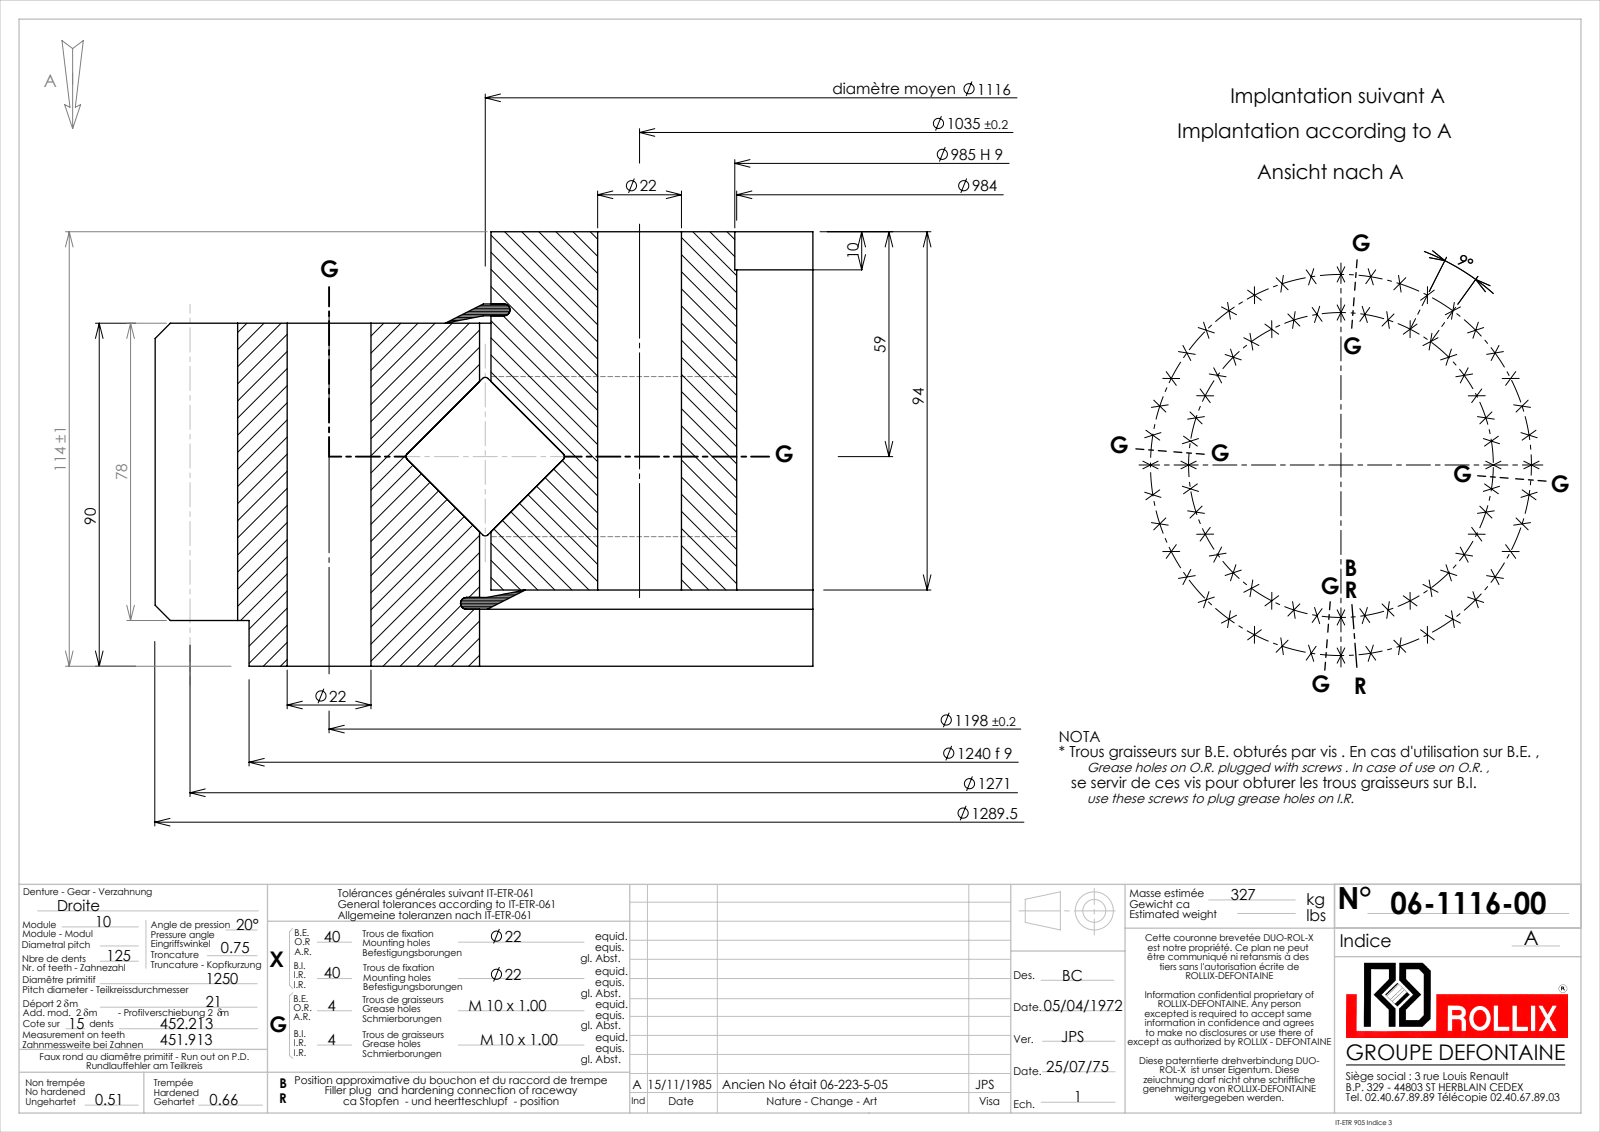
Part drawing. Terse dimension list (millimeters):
name: 06-1116-00
written by: SolidWorks 2016 (CONFIG_CONTROL_DESIGN)
unit: mm
bodies: 5 solids, 1016 faces (266 planar, 447 cylindrical, 303 other)
size: 1289.48 × 1289.4 × 114
volume: 39 280 000 mm³; area: 3 466 000 mm²
holes: 80× ⌀22, 8× ⌀9, 1× ⌀984, 1× ⌀985, 1× ⌀1119
bosses: 1× ⌀1240, 1× ⌀1113, 1× ⌀30
rounds: 1× R623, 1× R644.75
face distances: 90, 20, 70, 114, 94, 24, 1.95, 71.95, 3.1, 5.05
hole spacings: 187.41, 543.88, 279.67, 370.2, 625.95, 847.11, 93.99, 458.45
